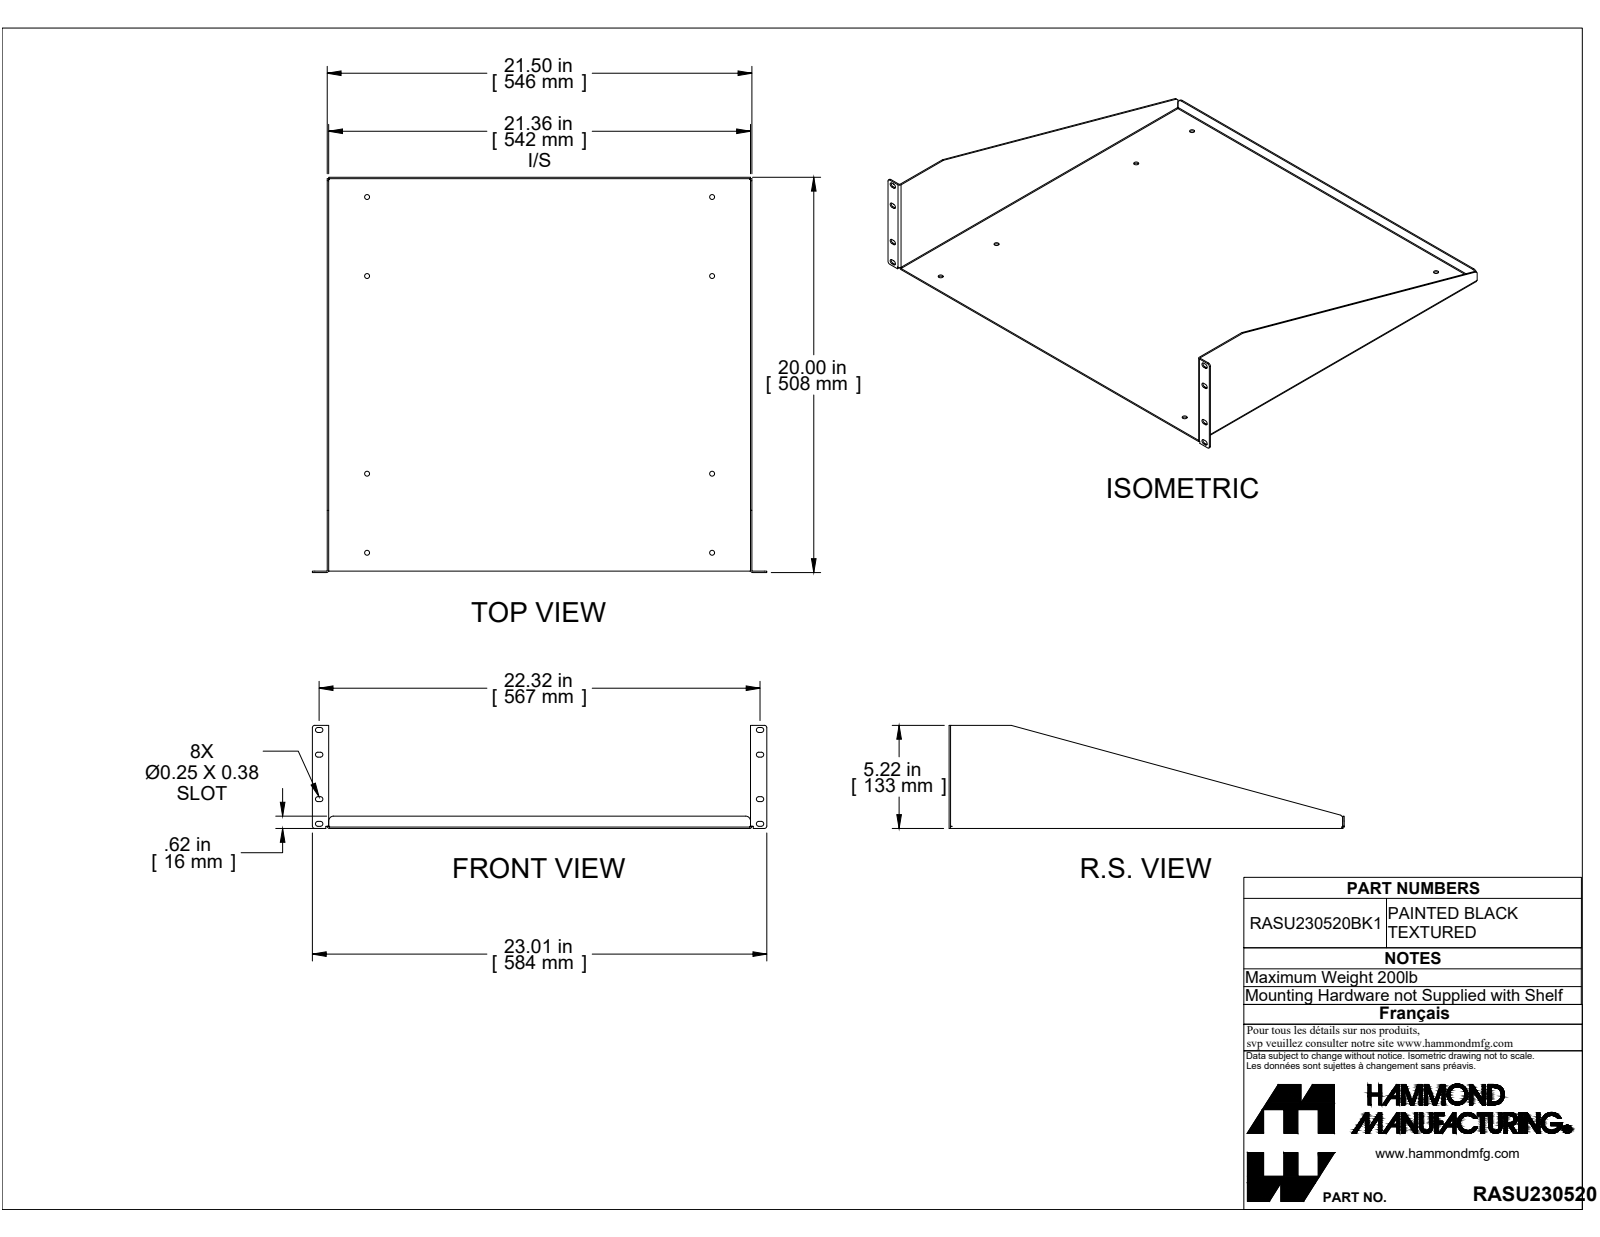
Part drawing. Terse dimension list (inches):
name: RASU230520BK1
written by: SolidWorks 2019 (CONFIG_CONTROL_DESIGN)
unit: in
bodies: 1 solid, 104 faces (56 planar, 44 cylindrical, 4 other)
size: 23.006 × 20 × 5.218
volume: 41.27 in³; area: 1 155 in²
holes: 8× ⌀0.25
rounds: 20× R0.125, 5× R0.036, 5× R0.108, 3× R0.055, 2× R0.25
face distances: 0.072, 21.428, 21.356, 21.5, 19.856, 19.928, 0.072, 19.928, 20, 0.625
hole spacings: 4, 14, 17.468, 17.92, 22.386, 10, 18, 20.128
